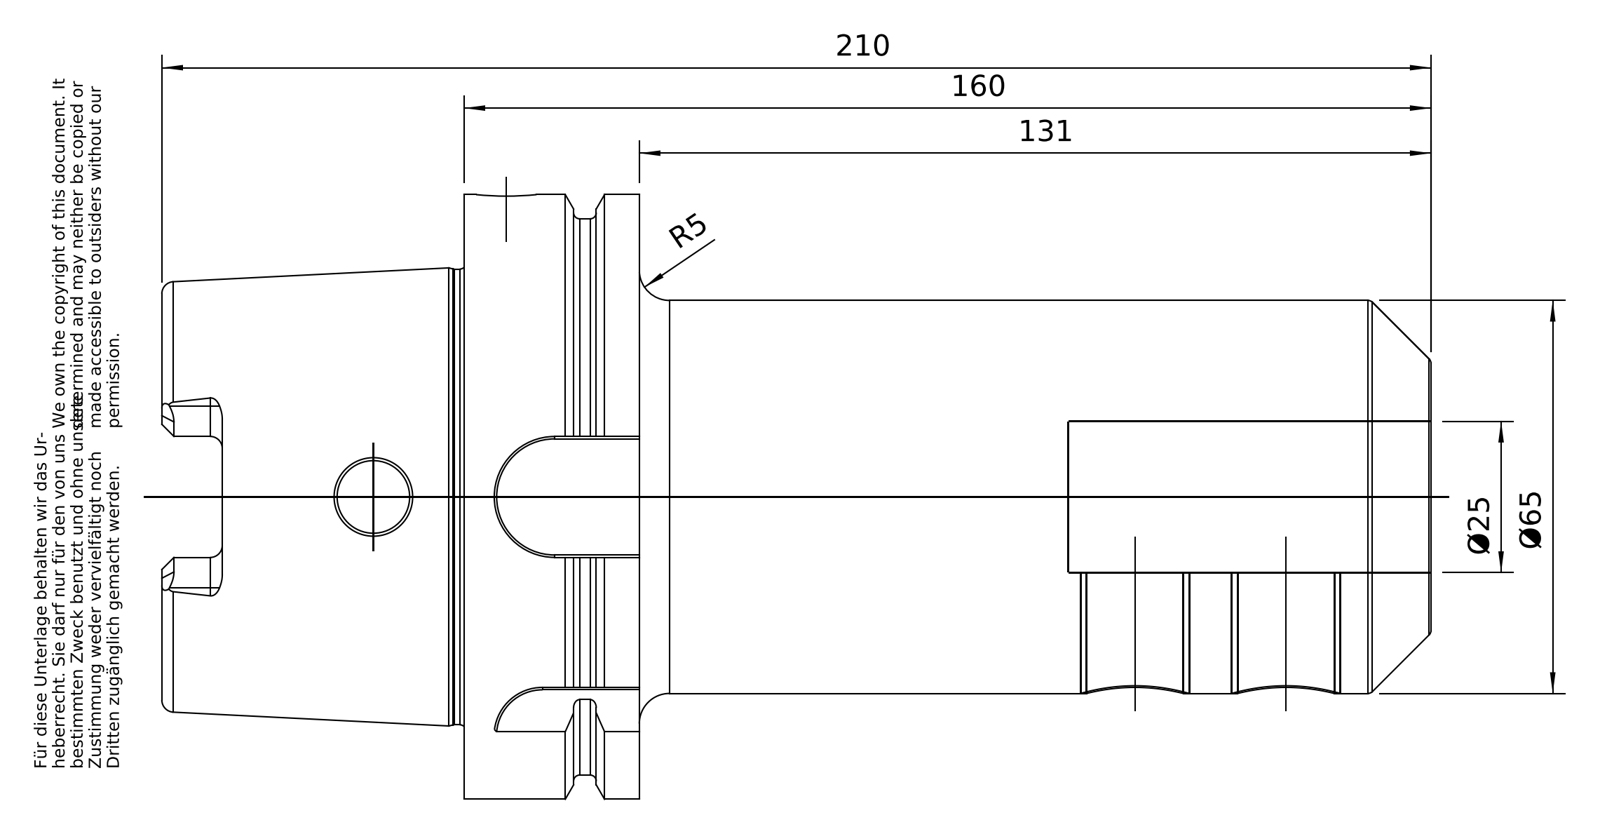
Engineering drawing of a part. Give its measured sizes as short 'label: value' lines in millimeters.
name: A100-002-25
written by: PRO/ENGINEER BY PARAMETRIC TECHNOLOGY CORPORATION, 2010430 (CONFIG_CONTROL_DESIGN)
unit: mm
bodies: 1 solid, 184 faces (50 planar, 59 cylindrical, 75 other)
size: 210 × 100 × 100
volume: 643 203 mm³; area: 83 597 mm²
holes: 2× ⌀16, 2× ⌀18, 1× ⌀10, 1× ⌀12, 1× ⌀22.5, 1× ⌀24, 1× ⌀24.32, 1× ⌀24.5, 1× ⌀25, 1× ⌀53, 1× ⌀63
bosses: 1× ⌀100, 1× ⌀92, 1× ⌀75.36, 1× ⌀65
rounds: 6× R2, 4× R5, 1× R8, 1× R10, 1× R11
face distances: 29, 12.5, 16.5, 160, 147.5, 131, 50, 62.5, 79, 210
hole spacings: 25, 104, 129
